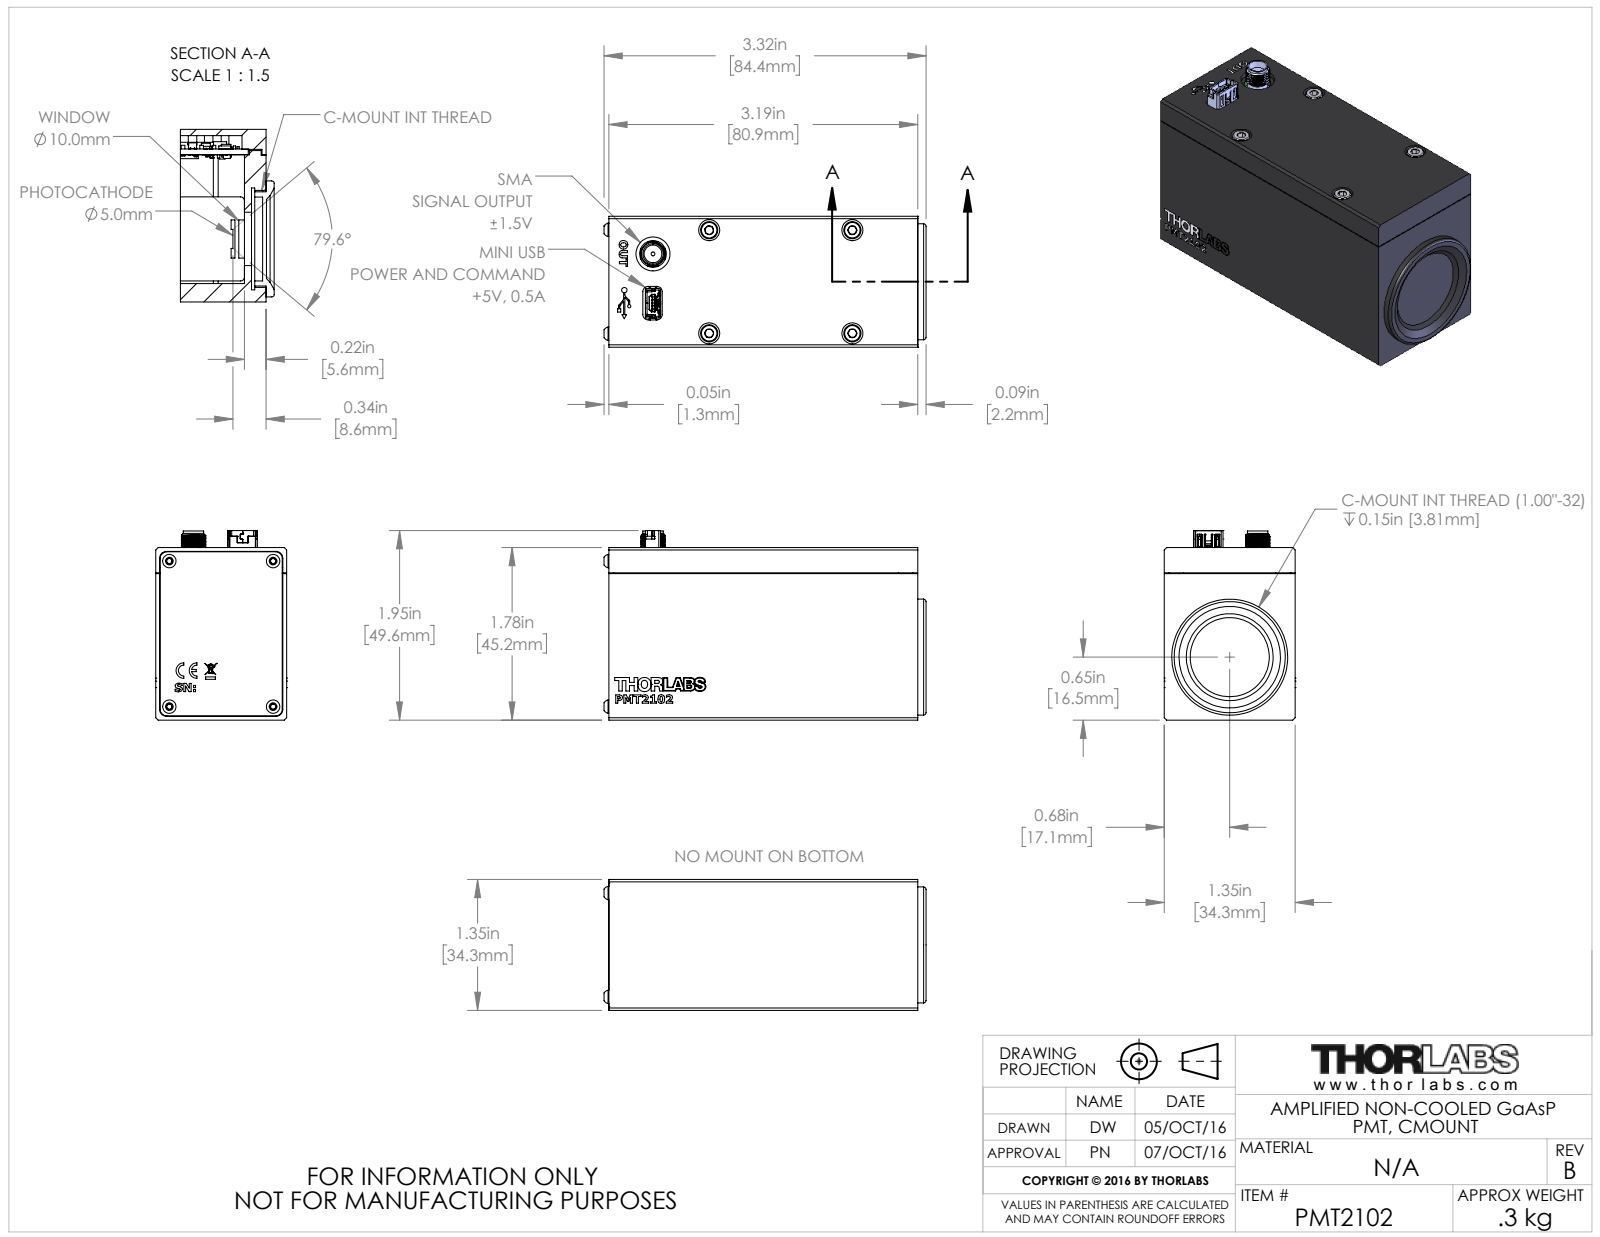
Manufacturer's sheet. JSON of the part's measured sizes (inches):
{"part_name": "TTN092855-E0W", "step_written_by": "SolidWorks 2016 (AUTOMOTIVE_DESIGN)", "units": "inches", "bodies": {"solids": 246, "faces": 7122, "planar": 3887, "cylindrical": 2280, "other": 955}, "overall_size": [3.321, 1.955, 1.35], "volume_in3": 5.625, "surface_area_in2": 78.9, "round_holes": [[0.063, 9], [0.094, 8], [0.024, 5], [0.067, 5], [0.114, 5], [0.081, 4], [0.173, 4], [0.217, 4], [0.016, 2], [0.035, 2], [0.079, 2], [0.197, 2]], "round_bosses_or_shafts": [[0.138, 9], [0.079, 8], [0.058, 8], [0.02, 8], [0.177, 4], [0.098, 4], [0.075, 4], [0.047, 4]], "partial_cylinders_radius": [[0.004, 87], [0.008, 34], [0.02, 24], [0.07, 20], [0.135, 20], [0.015, 10], [0.01, 6], [0.025, 6]], "face_to_face_distances": [0.215, 1.135, 1.35, 0.893, 0.027, 0.866, 1.78, 0.058, 0.92, 1.577], "hole_center_spacings": [0.145, 0.513, 0.551, 0.063, 0.078, 0.205, 0.39, 0.58]}
